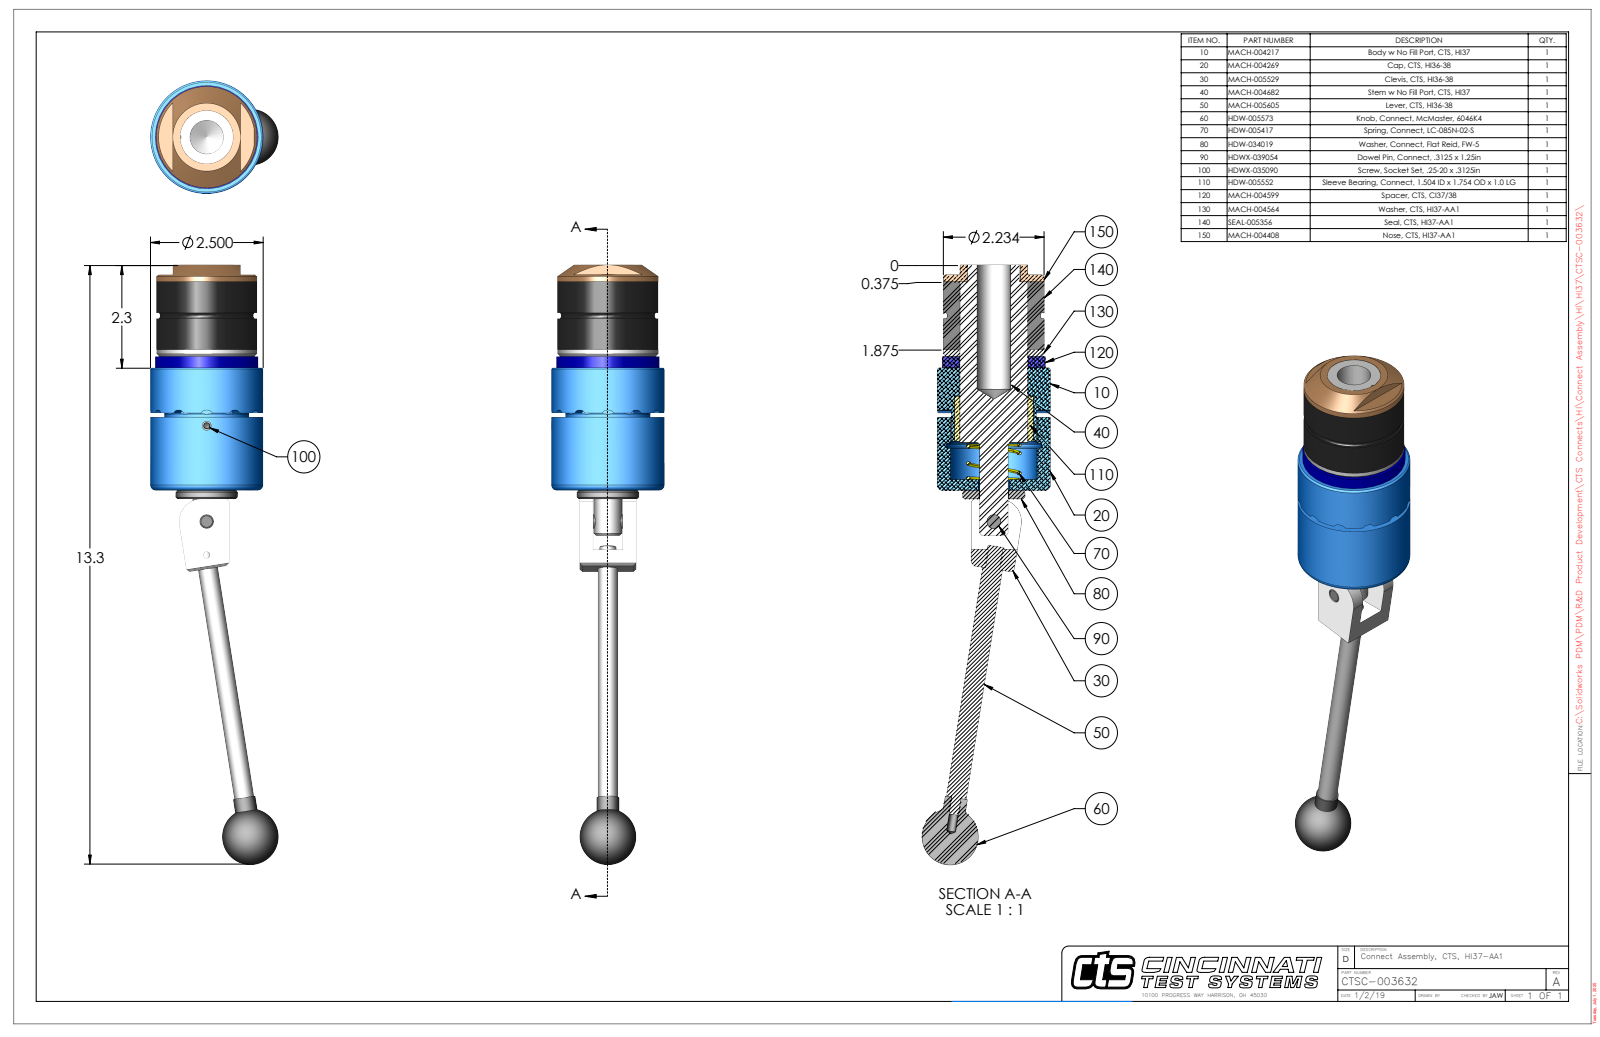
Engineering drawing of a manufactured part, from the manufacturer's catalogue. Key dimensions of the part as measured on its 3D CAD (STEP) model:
Part name (STEP PRODUCT): CTSC-003632
STEP written by: SolidWorks 2023 (AUTOMOTIVE_DESIGN)
Units: inches
Bodies: 10 solids, 279 faces (98 planar, 110 cylindrical, 71 other)
Overall size (bounding box): 13.275 × 2.843 × 2.5
Volume: 23.95 in³ · Surface area: 130 in²
Round holes (diameter × count): ⌀0.201 ×2, ⌀0.15 ×1, ⌀0.311 ×1, ⌀0.313 ×1, ⌀0.314 ×1, ⌀0.656 ×1, ⌀0.696 ×1, ⌀0.75 ×1, ⌀1.172 ×1, ⌀1.495 ×1, ⌀1.501 ×1, ⌀1.51 ×1
Round bosses / shafts (diameter × count): ⌀2.5 ×1, ⌀2.281 ×1, ⌀2.234 ×1, ⌀1.875 ×1, ⌀1.5 ×1, ⌀1.496 ×1, ⌀1.38 ×1, ⌀1.25 ×1
Partial cylindrical surfaces — rounded edges, fillets, slot ends (radius × count): R0.12 ×12, R0.029 ×2, R0.5 ×1, R1.209 ×1
Main face-to-face distances: 1.902, 2.713, 4.615, 1.5, 3.115, 0.402, 0.25, 2.963, 0.152, 1.652
Hole centre spacings: 0.74, 2.118, 2.858
